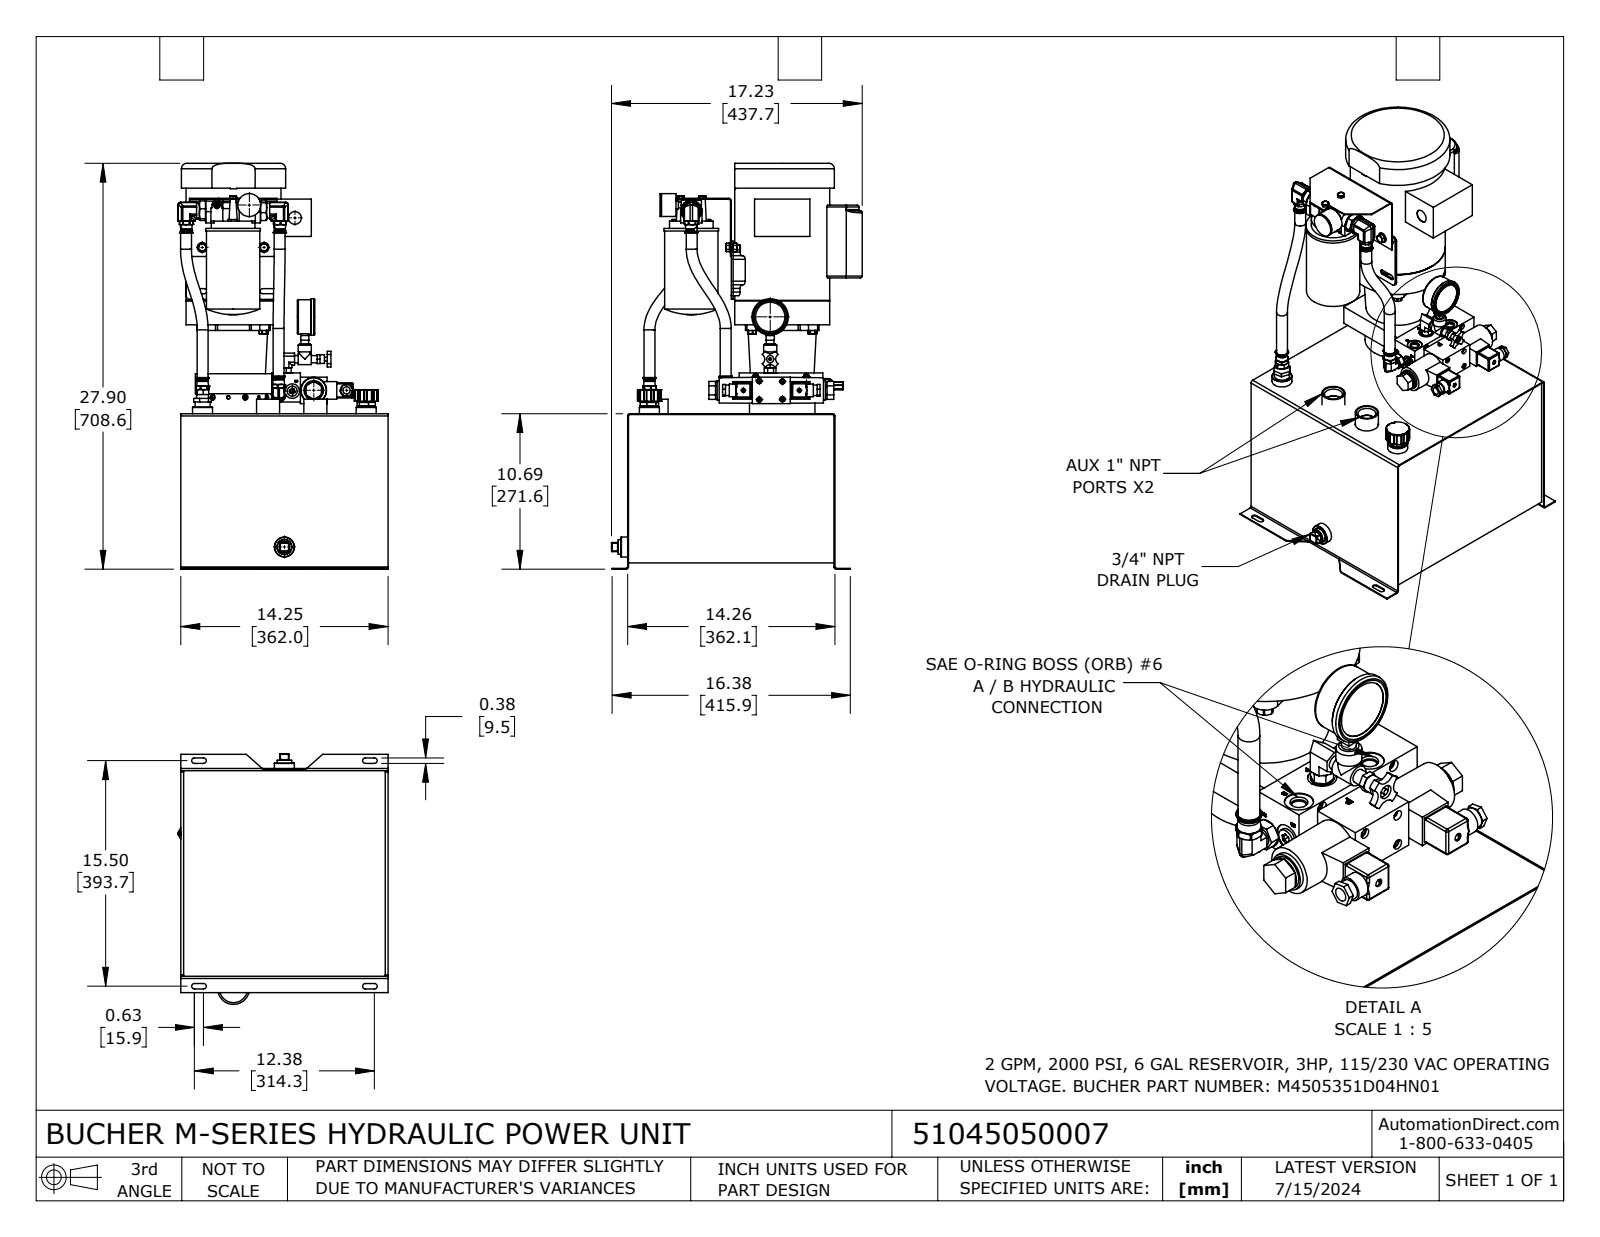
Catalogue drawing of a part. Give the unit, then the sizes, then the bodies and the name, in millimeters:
Units: millimetres
Overall size (bounding box): 708.6 × 437.7 × 367.1
Round holes (diameter × count): ⌀6.4 ×9, ⌀25.4 ×9, ⌀8 ×8, ⌀11.9 ×8, ⌀13 ×8, ⌀5.7 ×6, ⌀12.7 ×6, ⌀7.1 ×5, ⌀4.3 ×4, ⌀5.8 ×4, ⌀6.8 ×4, ⌀7.4 ×4
Round bosses / shafts (diameter × count): ⌀6.2 ×7, ⌀9.3 ×6, ⌀4.7 ×6, ⌀19.1 ×5, ⌀22.9 ×4, ⌀18.7 ×4, ⌀11.7 ×4, ⌀9.4 ×4
Partial cylindrical surfaces — rounded edges, fillets, slot ends (radius × count): R0.6 ×24, R1 ×24, R1.3 ×24, R0.5 ×20, R6.4 ×16, R1.8 ×14, R3 ×13, R1 ×12
Main face-to-face distances: 3.2, 1.7, 360.5, 260.4, 257.2, 258.7, 255.5, 1.7, 362.1, 351.8
Hole centre spacings: 74.6, 111.3, 40, 53.3, 23.3, 45.2, 45.2, 55.7
Volume: 12 710 000 mm³ · Surface area: 2 206 000 mm²
Bodies: 56 solids, 3407 faces (1376 planar, 1088 cylindrical, 943 other)
Part name (STEP PRODUCT): 51045050007
STEP written by: SolidWorks 2023 (CONFIG_CONTROL_DESIGN)
